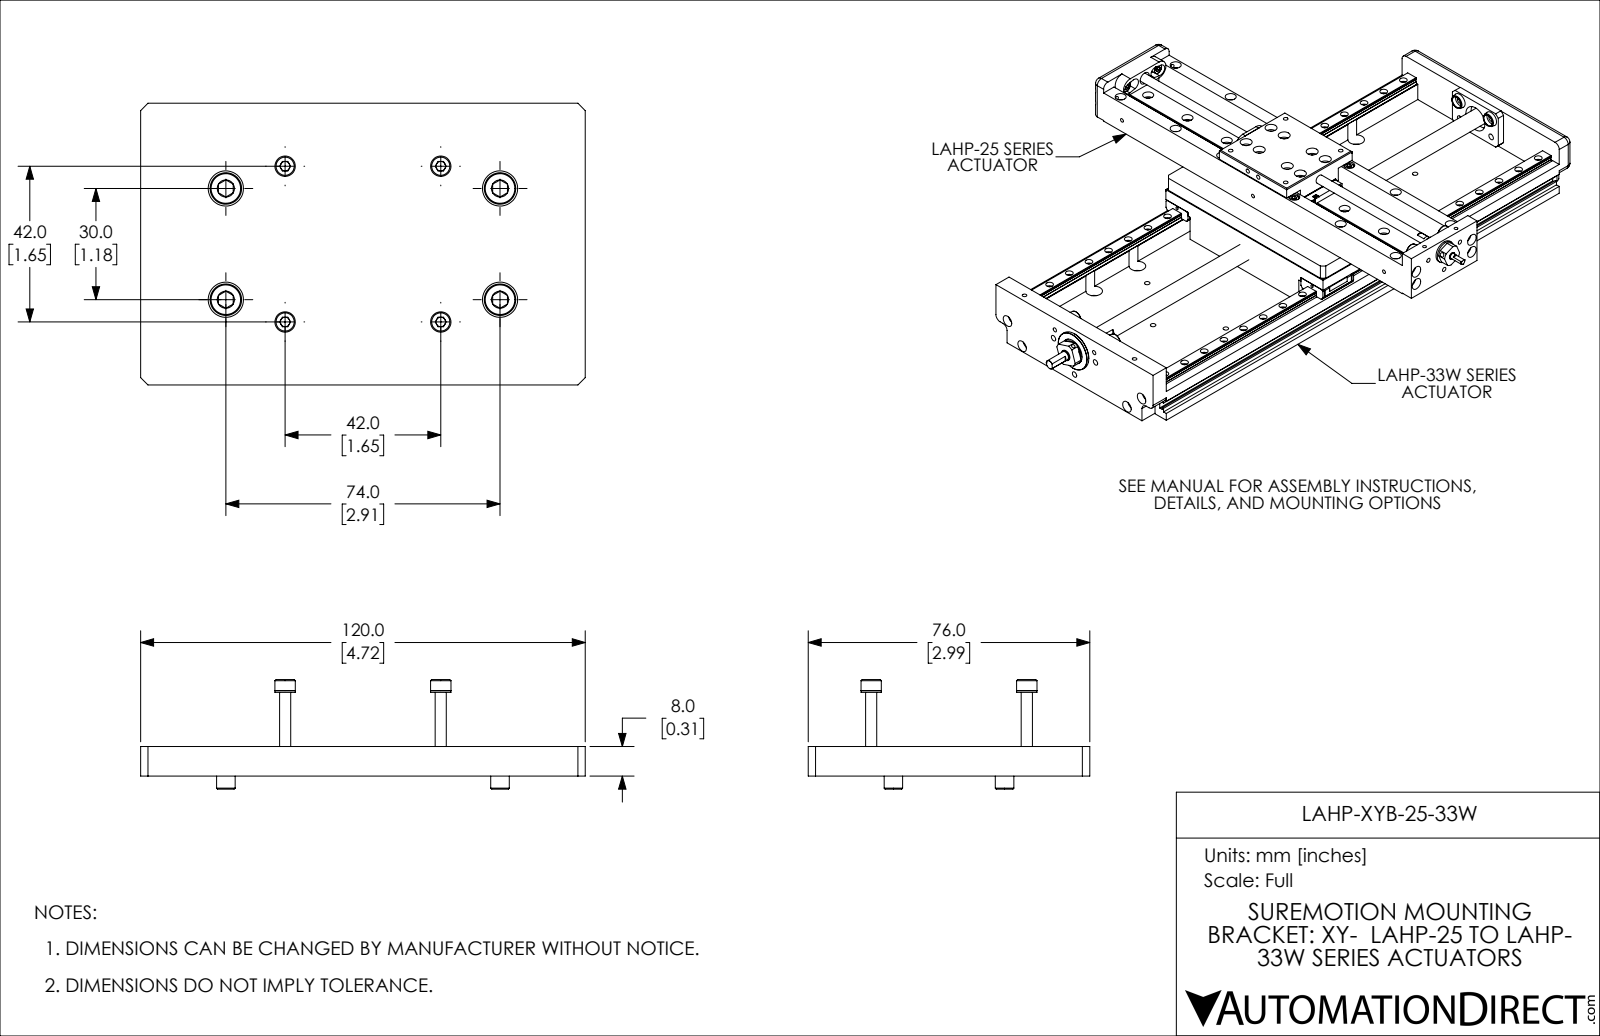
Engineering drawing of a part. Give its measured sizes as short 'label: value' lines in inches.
name: LAHP-XYB-25-33W
written by: SolidWorks 2019 (CONFIG_CONTROL_DESIGN)
unit: in
bodies: 13 solids, 278 faces (122 planar, 72 cylindrical, 84 other)
size: 4.724 × 2.992 × 1.163
volume: 4.468 in³; area: 38.77 in²
holes: 4× ⌀0.098, 4× ⌀0.126, 4× ⌀0.217, 4× ⌀0.374
bosses: 4× ⌀0.335, 4× ⌀0.217, 4× ⌀0.197, 4× ⌀0.118
face distances: 0.315, 2.992, 4.724, 0.098, 0.217, 0.295, 0.197, 0.02, 0.907, 0.809
hole spacings: 0.673, 1.551, 1.654, 2.296, 2.687, 1.181, 2.339, 2.913
